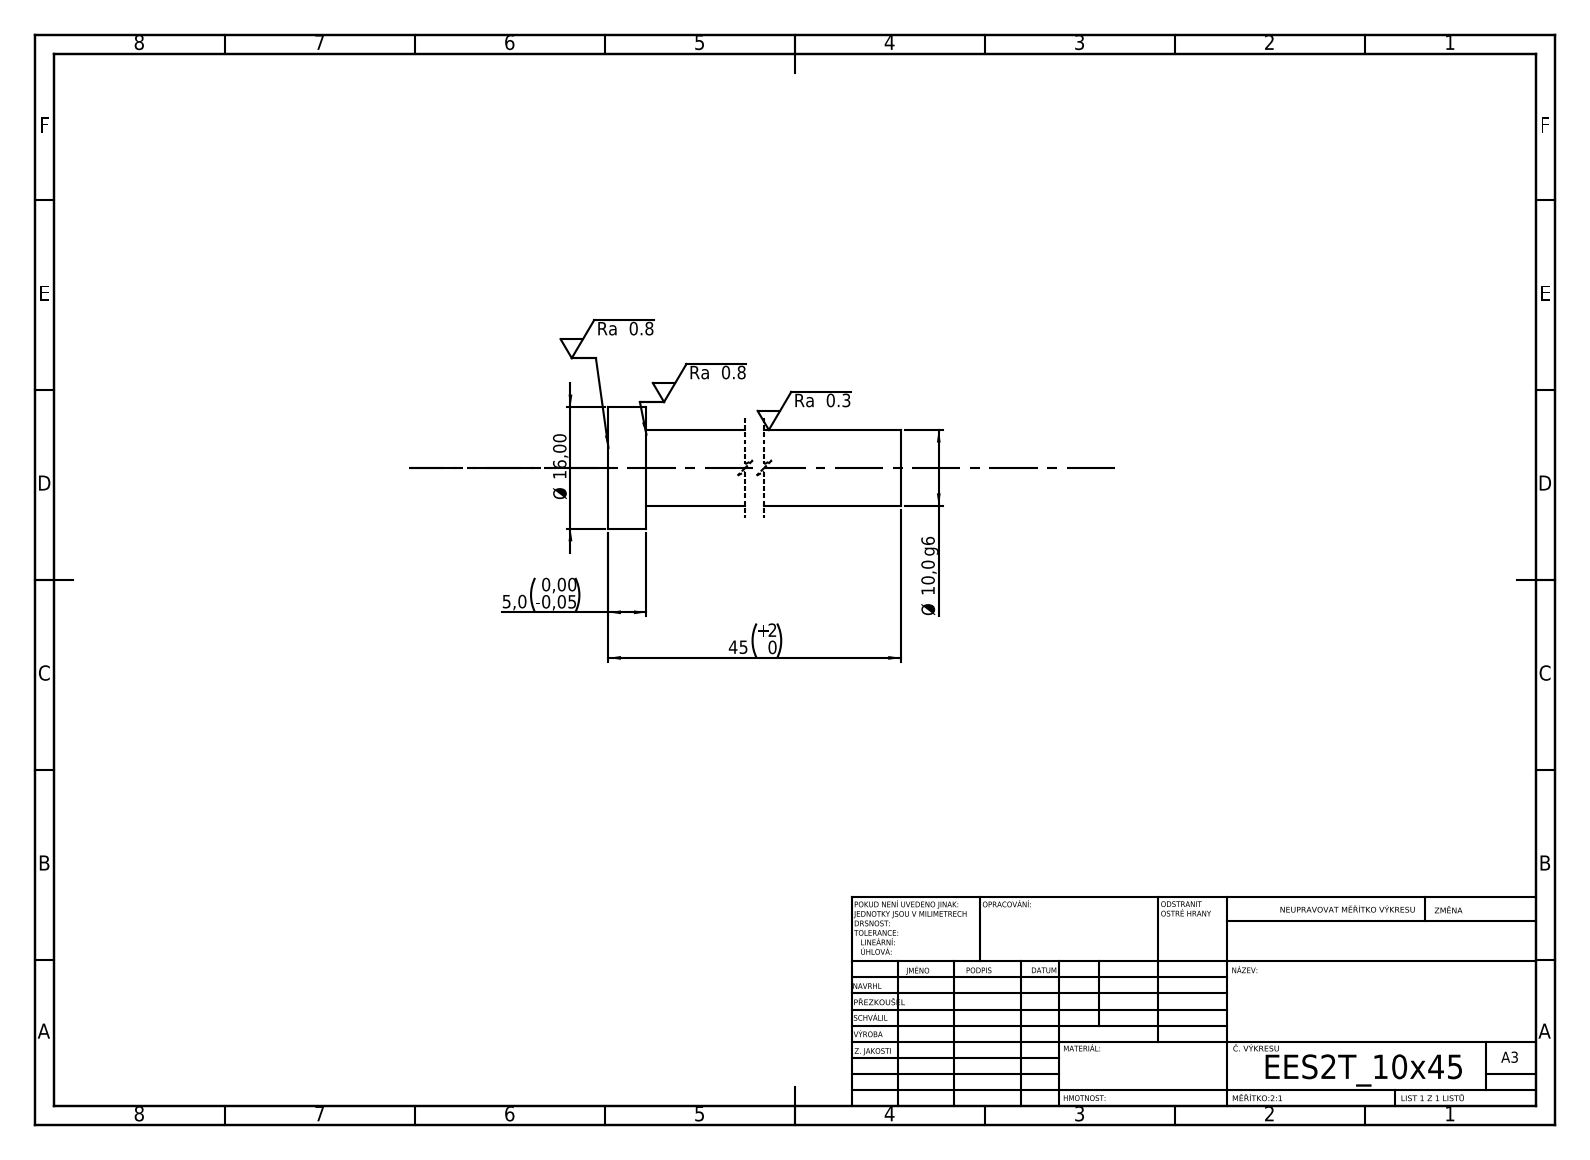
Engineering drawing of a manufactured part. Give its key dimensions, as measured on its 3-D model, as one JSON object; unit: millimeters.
{"step_written_by": "SolidWorks 2019 (CONFIG_CONTROL_DESIGN)", "units": "millimeters", "bodies": {"solids": 1, "faces": 7, "planar": 3, "cylindrical": 4, "other": 0}, "overall_size": [45, 16, 16], "volume_mm3": 4147, "surface_area_mm2": 1910, "round_bosses_or_shafts": [[16, 1], [10, 1]], "face_to_face_distances": [5, 45, 40]}
